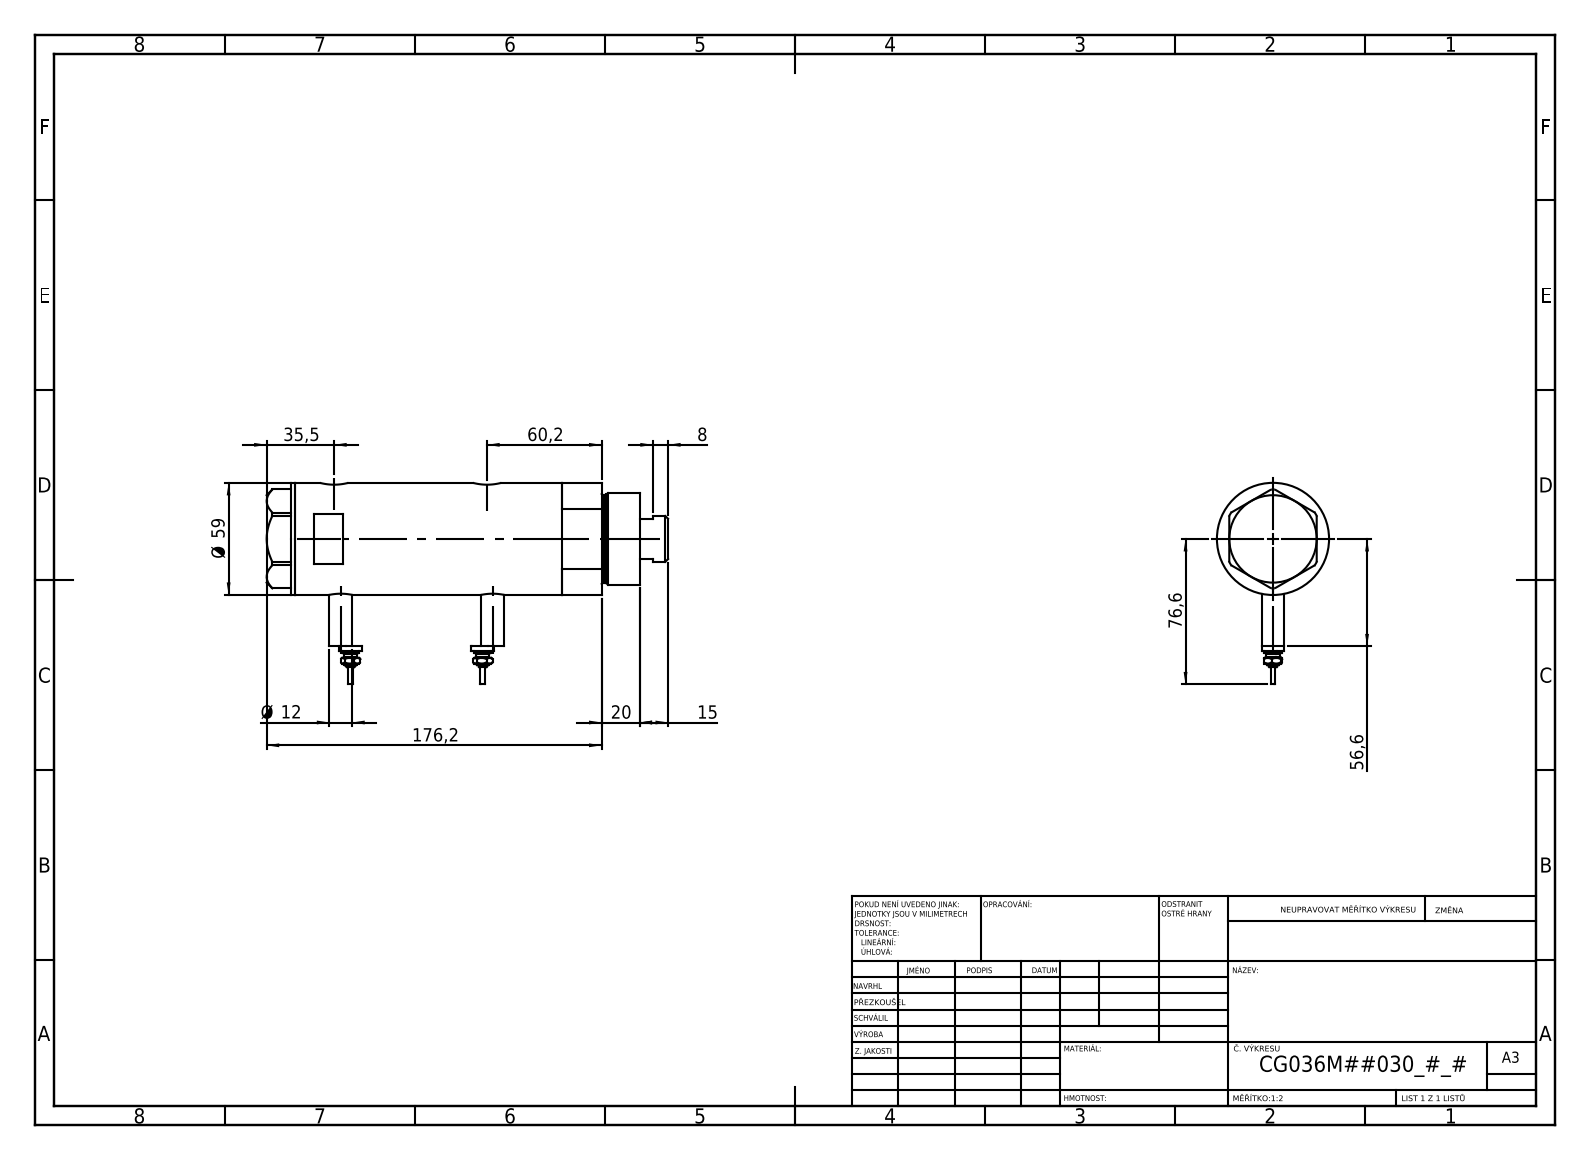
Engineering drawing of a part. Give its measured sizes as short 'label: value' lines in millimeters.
name: V270CG_VC; Switch; V270CG_BACK; V270CG_FRONT (+1 more)
written by: SolidWorks 2019 (CONFIG_CONTROL_DESIGN)
unit: mm
bodies: 6 solids, 212 faces (79 planar, 69 cylindrical, 64 other)
size: 211.2 × 106.1 × 59
volume: 494 998 mm³; area: 103 444 mm²
holes: 2× ⌀9.73, 2× ⌀12.5, 2× ⌀15, 1× ⌀8.5, 1× ⌀25, 1× ⌀26.5, 1× ⌀36, 1× ⌀40, 1× ⌀52
bosses: 4× ⌀12, 2× ⌀9, 2× ⌀7, 2× ⌀4.5, 2× ⌀2.5, 1× ⌀59, 1× ⌀48, 1× ⌀46
face distances: 102.2, 23.5, 78.7, 15, 38.5, 117.2, 2, 196.2, 181.2, 157.7
hole spacings: 2.9, 3.5, 77, 79.9, 80.5, 83.4
